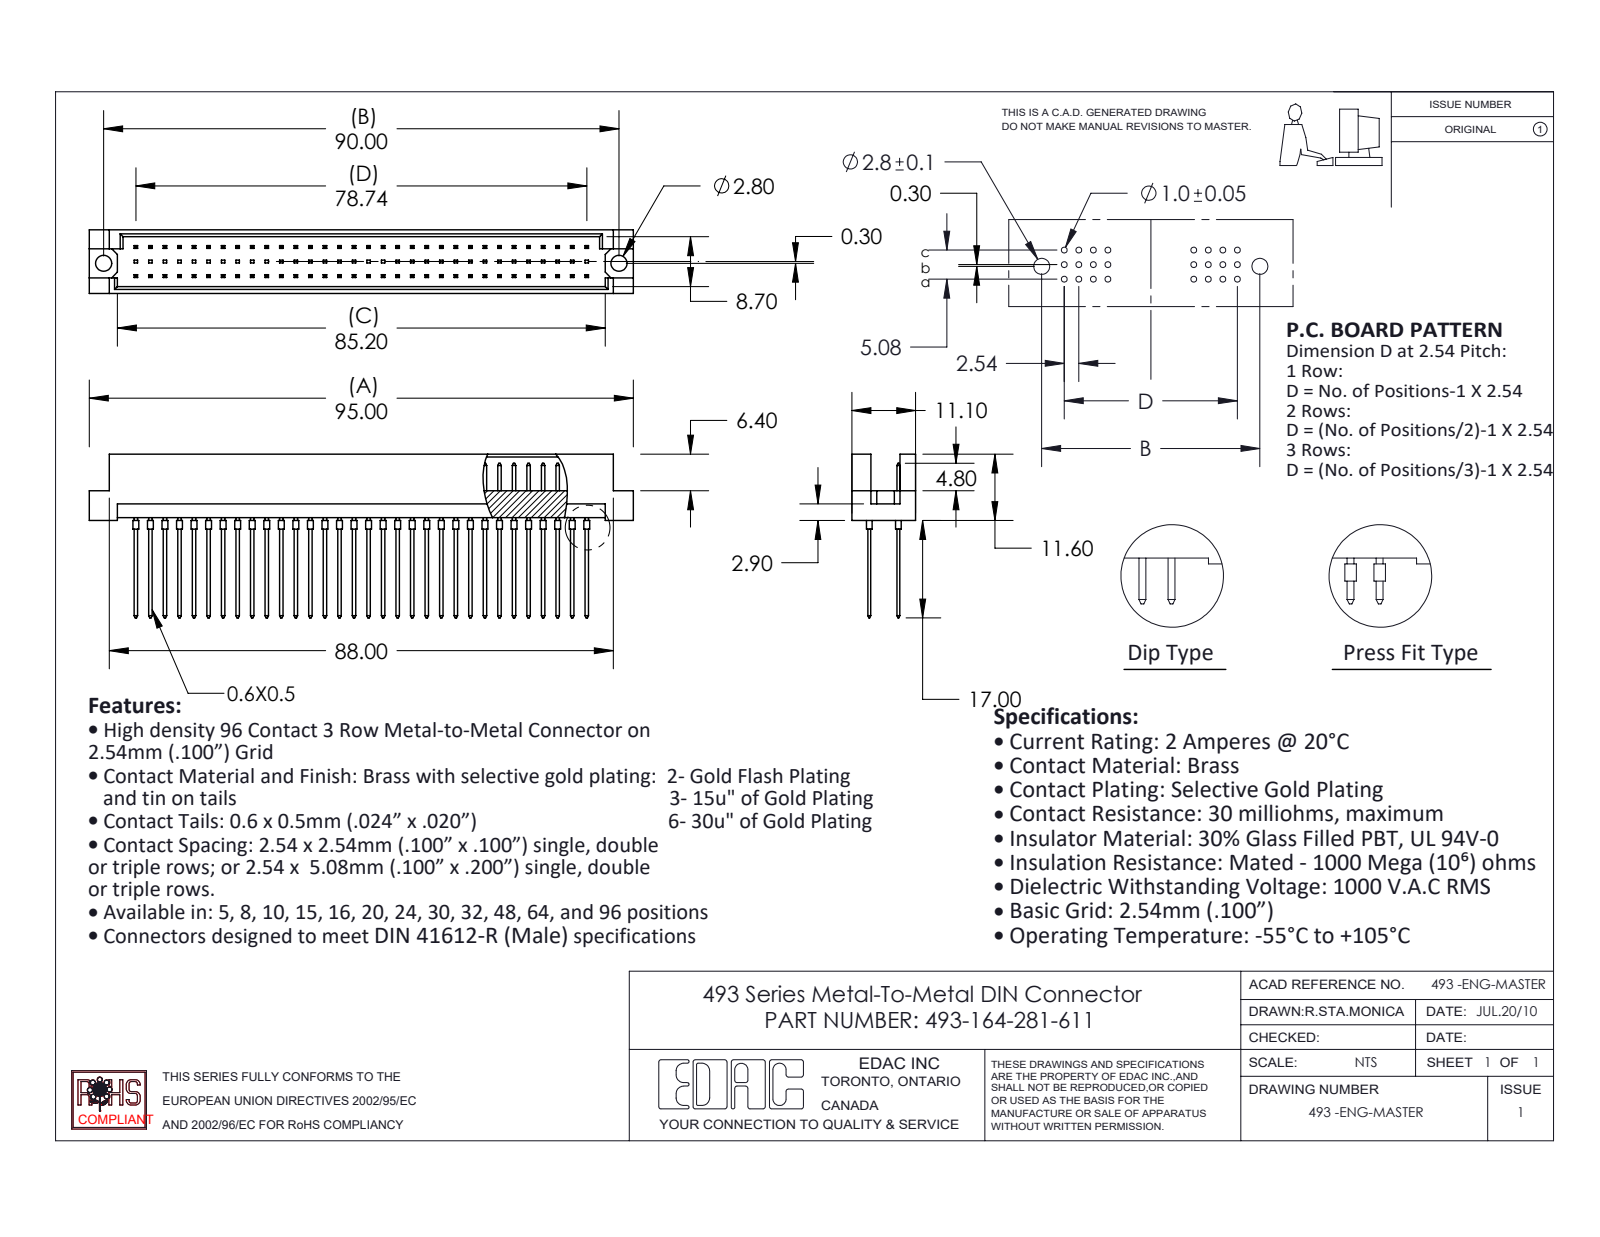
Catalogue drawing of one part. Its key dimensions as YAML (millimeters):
part_name: "493 Part_96; 493-290_81; 493-164-281-611"
step_written_by: "SolidWorks 2020 (CONFIG_CONTROL_DESIGN)"
units: millimeters
bodies: {solids: 65, faces: 1844, planar: 1712, cylindrical: 132, other: 0}
overall_size: [95, 28.6, 11.1]
volume: 6217
surface_area: 10404
round_holes:
  - {diameter: 2.8, count: 2}
round_bosses_or_shafts:
  - {diameter: 1, count: 64}
face_to_face_distances: [5.08, 1.2, 9.9, 0.5, 2.76, 3.26, 7.84, 8.34, 1.56, 2.06]
hole_center_spacings: [90]
